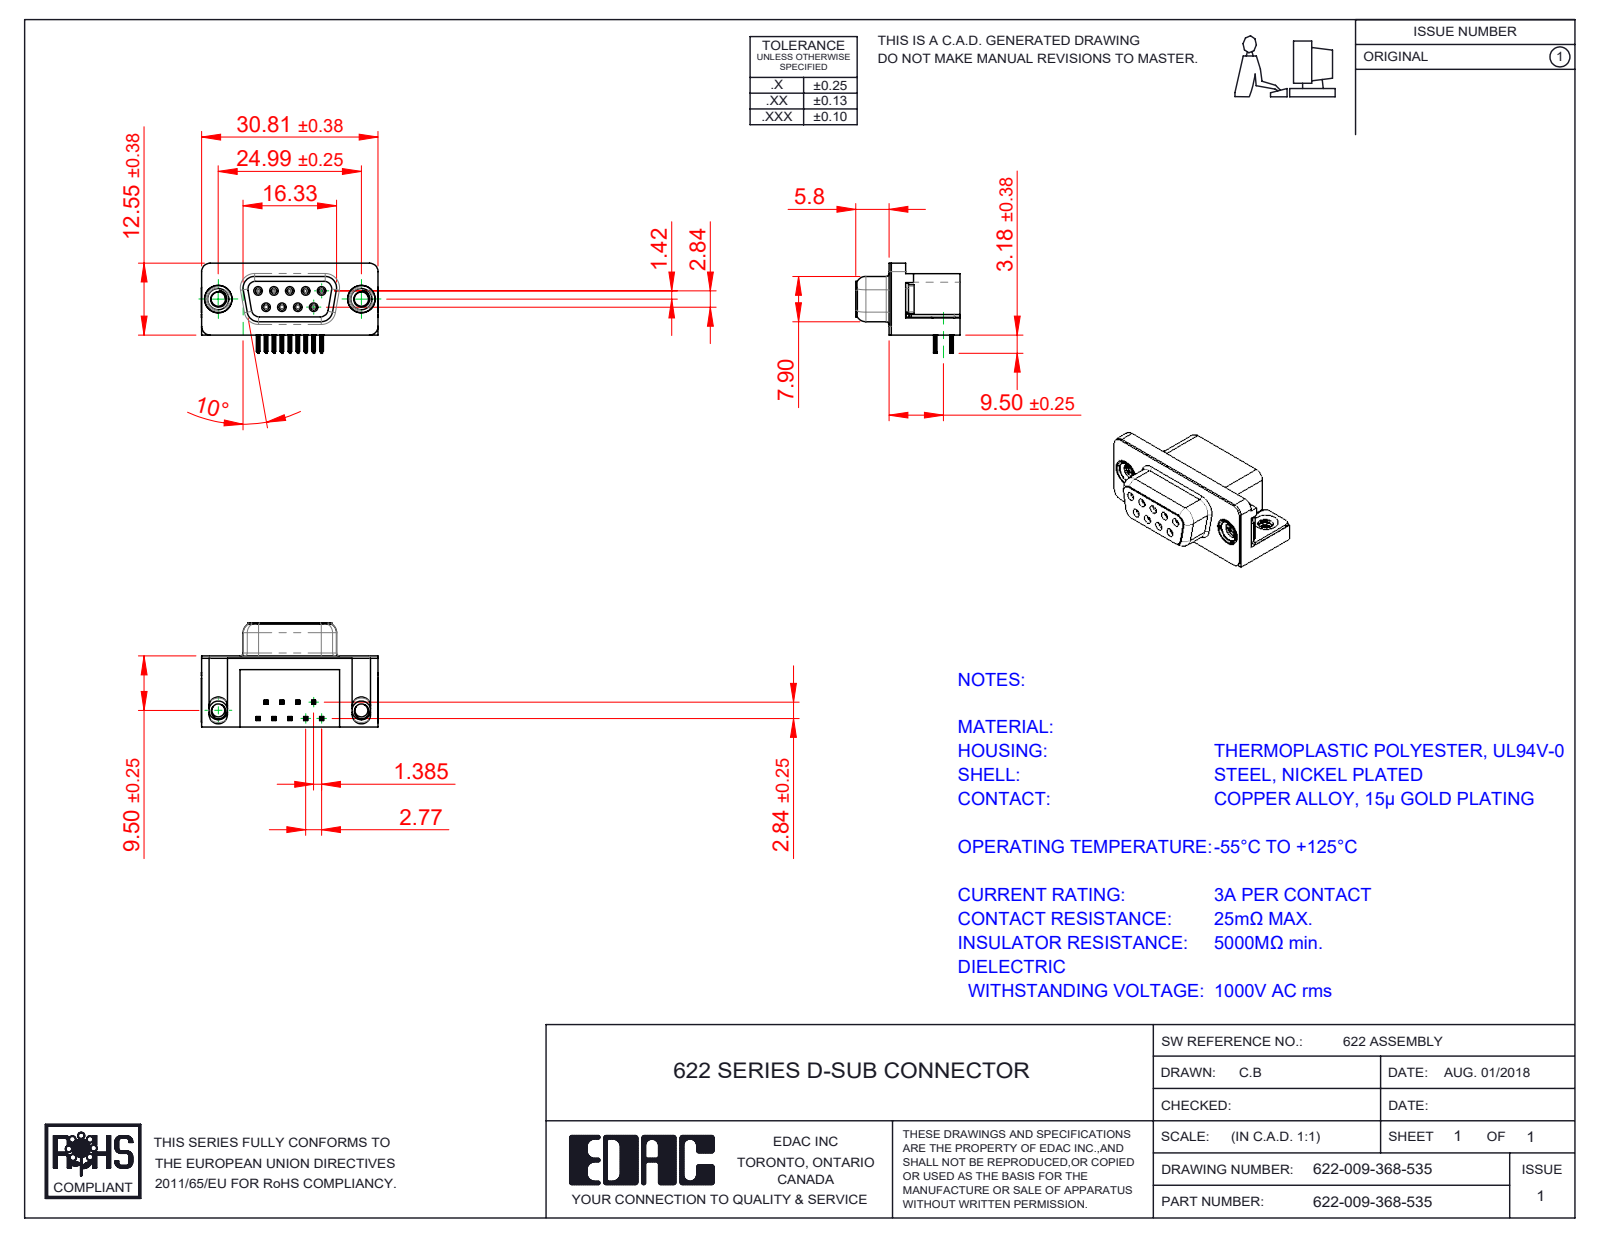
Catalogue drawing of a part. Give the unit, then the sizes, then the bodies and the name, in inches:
Units: inches
Overall size (bounding box): 1.216 × 0.717 × 0.64
Round holes (diameter × count): ⌀0.031 ×9, ⌀0.035 ×9, ⌀0.098 ×2, ⌀0.157 ×2, ⌀0.189 ×2, ⌀0.197 ×2
Round bosses / shafts (diameter × count): ⌀0.047 ×9, ⌀0.193 ×2, ⌀0.187 ×2, ⌀0.154 ×2
Partial cylindrical surfaces — rounded edges, fillets, slot ends (radius × count): R0.004 ×72, R0.006 ×36, R0.014 ×18, R0.039 ×18, R0.02 ×10, R0.013 ×9, R0.01 ×8, R0.053 ×8
Main face-to-face distances: 0.016, 0.472, 0.488, 0.014, 0.114, 0.098, 0.244, 0.407, 0.02, 0.374
Hole centre spacings: 0.124, 0.109, 0.218, 0.198, 0.198, 0.327, 0.294, 0.295
Volume: 0.227 in³ · Surface area: 7.877 in²
Bodies: 15 solids, 1612 faces (716 planar, 428 cylindrical, 468 other)
Part name (STEP PRODUCT): 622 Contact Top; 622-009-368-535; 622 M3 Threaded Rivet; 622 2 Prong Board Lock (+3 more)
STEP written by: SolidWorks 2016 (CONFIG_CONTROL_DESIGN)
